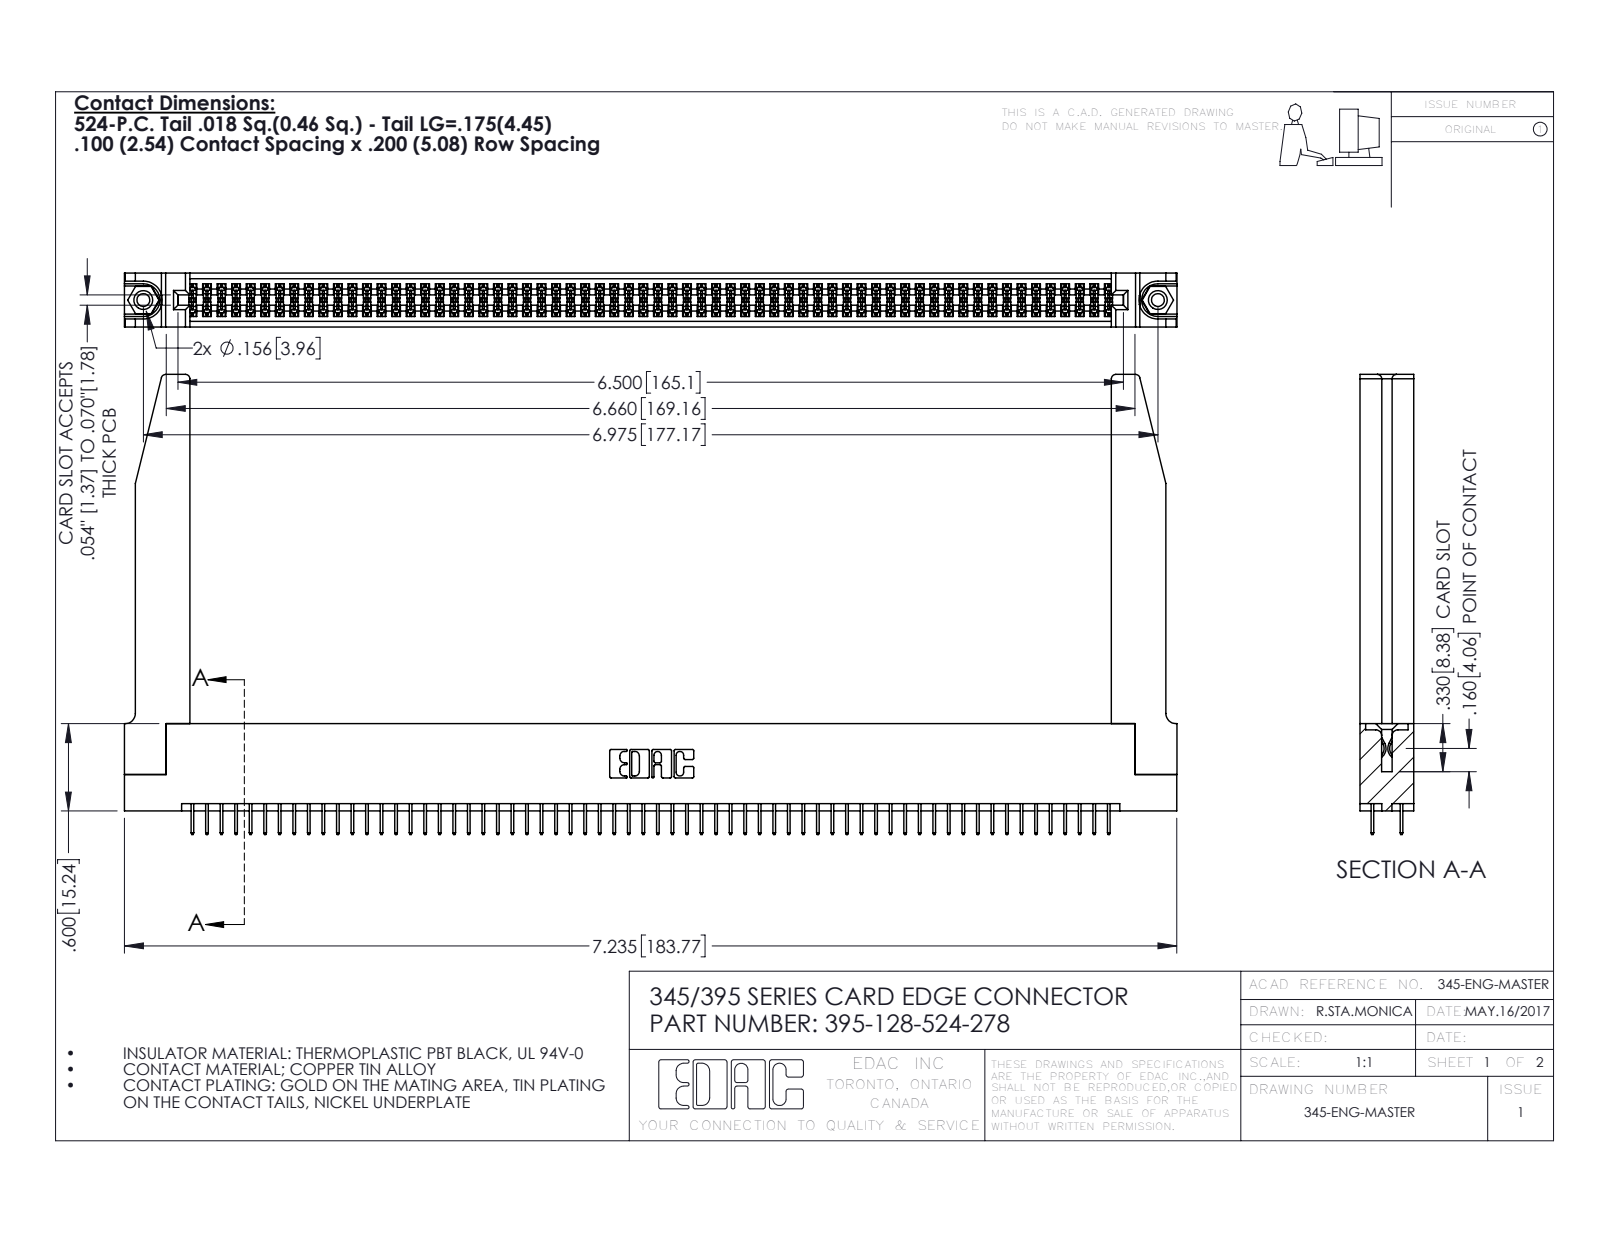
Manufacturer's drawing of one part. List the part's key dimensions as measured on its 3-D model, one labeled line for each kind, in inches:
Part name (STEP PRODUCT): 345-220-078_345-220-078; 345-250-001_345-250-001-102; 345-292-001_345-293-124; 395-128-524-278 (+1 more)
STEP written by: SolidWorks 2016 (CONFIG_CONTROL_DESIGN)
Units: inches
Bodies: 133 solids, 7272 faces (5214 planar, 2006 cylindrical, 52 other)
Overall size (bounding box): 7.236 × 3.162 × 0.37
Volume: 1.564 in³ · Surface area: 51.4 in²
Round holes (diameter × count): ⌀0.089 ×2, ⌀0.125 ×2, ⌀0.156 ×2, ⌀0.064 ×1
Round bosses / shafts (diameter × count): ⌀0.155 ×2
Partial cylindrical surfaces — rounded edges, fillets, slot ends (radius × count): R0.006 ×192, R0.01 ×22, R0.03 ×8, R0.007 ×6, R0.031 ×6, R0.026 ×3, R0.014 ×2, R0.019 ×2
Main face-to-face distances: 0.072, 0.37, 0.298, 0.2, 0.098, 0.272, 0.025, 0.225, 0.072, 0.175
Hole centre spacings: 0.27, 6.739, 6.975
